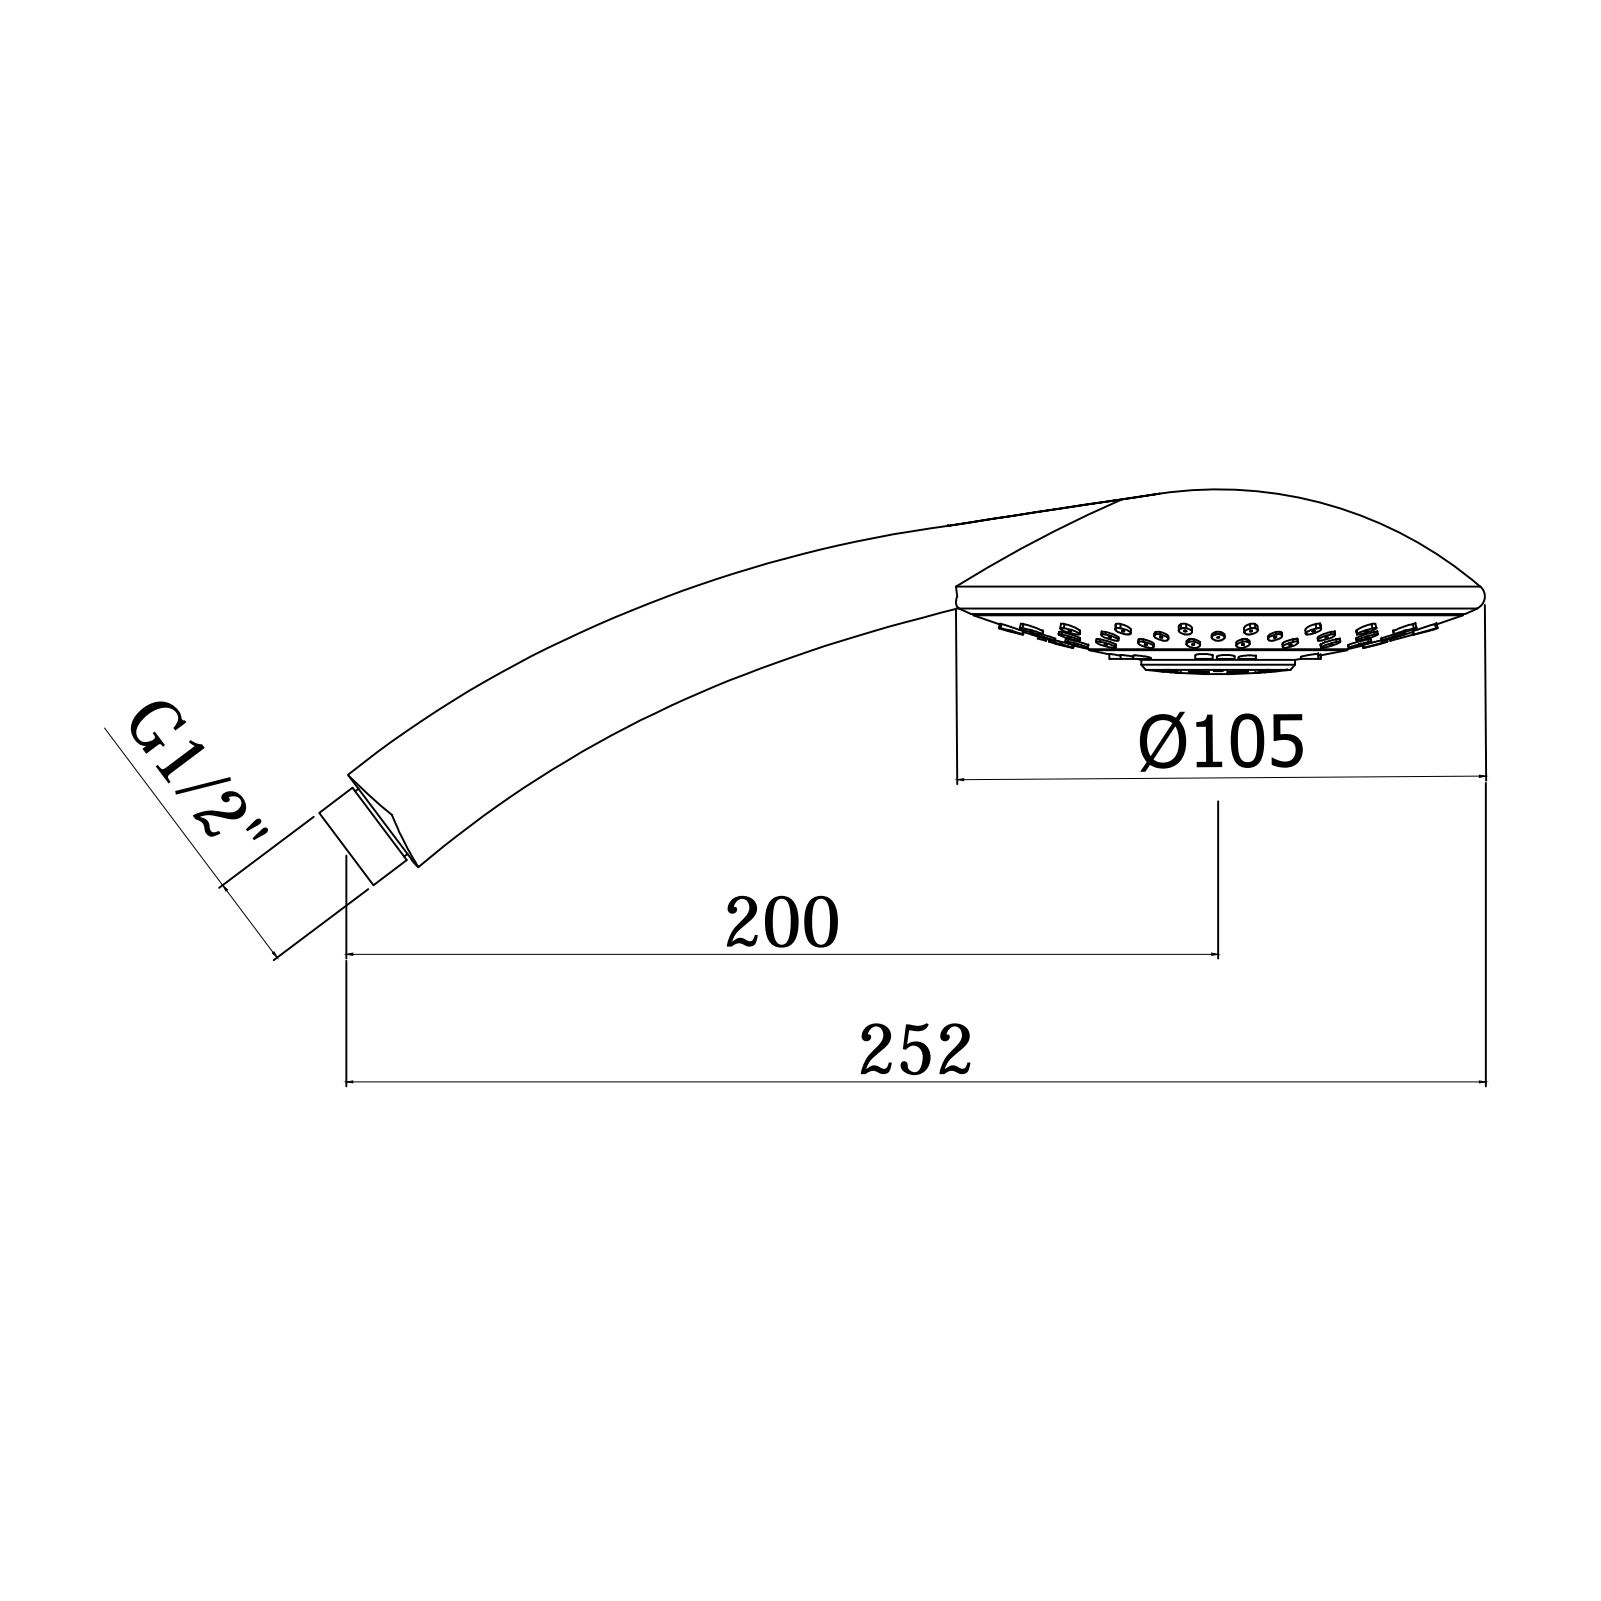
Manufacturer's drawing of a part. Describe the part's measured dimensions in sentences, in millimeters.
The part is named "ZDOC085CR". Its 3-D file was written by "CREO PARAMETRIC BY PTC INC, 2020044 (CONFIG_CONTROL_DESIGN)". It is 1 solid with 1401 faces: 157 planar, 257 cylindrical and 987 other. Overall it measures 241.97 by 104.19 by 90.95 millimeters. Its volume is 150 476 cubic millimeters and its surface area 76 734 square millimeters. Round holes: 50 of diameter 5, 2 of diameter 15, 1 of diameter 4.5, 1 of diameter 9.8, 1 of diameter 11, 1 of diameter 11.65, 1 of diameter 14, 1 of diameter 17.7, 1 of diameter 86.6, 1 of diameter 90.2, 1 of diameter 94.6, 1 of diameter 95.6. Round bosses or shafts: 1 of diameter 95, 1 of diameter 92.6, 1 of diameter 20.8, 1 of diameter 18.4, 1 of diameter 18, 1 of diameter 16.7, 1 of diameter 14. Partial cylindrical surfaces (rounded edges, fillets, slot ends): 1 of radius 5.9, 1 of radius 7.3, 1 of radius 9.25, 1 of radius 433.62. The main face-to-face distances are 2.5, 1.71, 0.79, 0.65, 2, 4.5, 2.79, 3.85, 2.14, 1.35. The hole center spacings are 39, 12.2, 24.1, 8, 18.34, 18.54, 31, 31.55.
